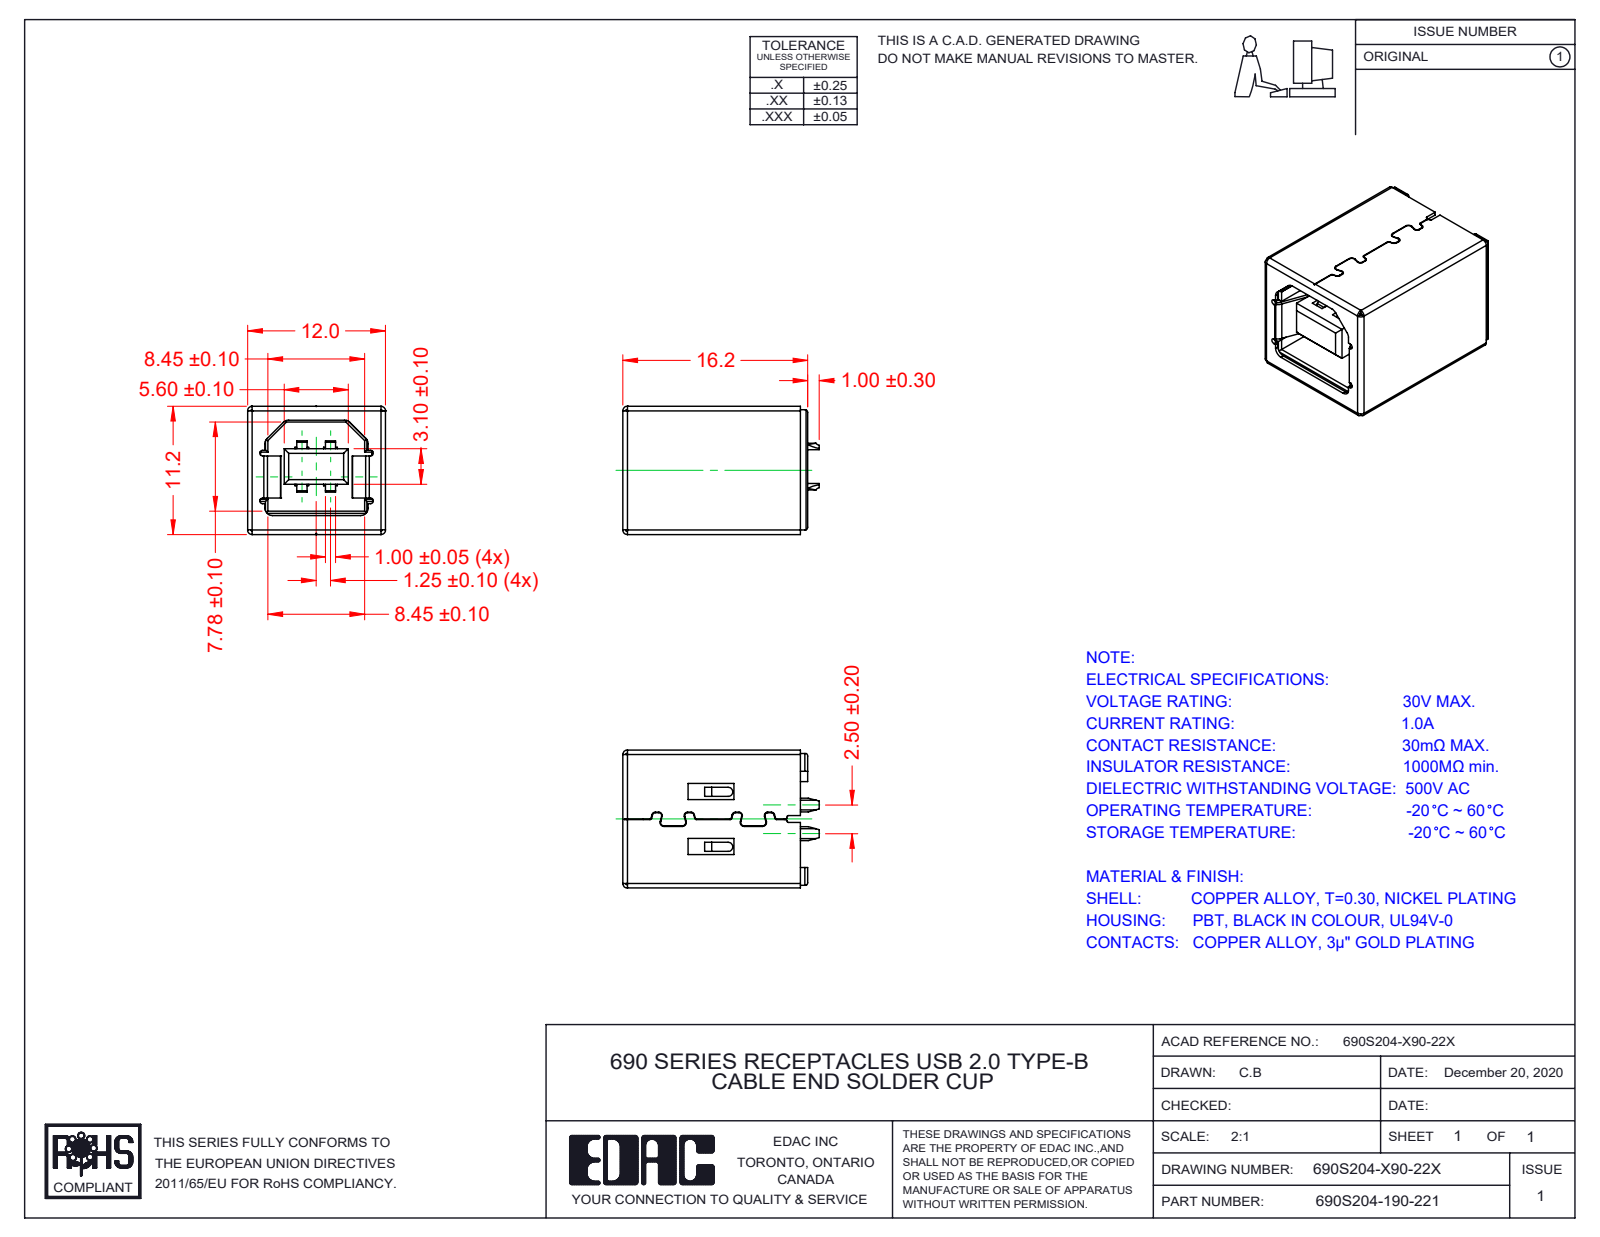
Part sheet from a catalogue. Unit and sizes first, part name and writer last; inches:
Units: inches
Overall size (bounding box): 0.675 × 0.474 × 0.441
Partial cylindrical surfaces — rounded edges, fillets, slot ends (radius × count): R0.01 ×19, R0.012 ×14, R0.016 ×12, R0.004 ×11, R0.008 ×8, R0.014 ×8, R0.006 ×6, R0.026 ×6
Main face-to-face distances: 0.429, 0.462, 0.417, 0.453, 0.45, 0.465, 0.474, 0.441, 0.081, 0.016
Volume: 0.083 in³ · Surface area: 5.234 in²
Bodies: 6 solids, 629 faces (428 planar, 201 cylindrical, 0 other)
Part name (STEP PRODUCT): Shell 690S204-X90-22X; Contact 690S204-X90-22X; Insulator 690S204-X90-22X_Black; 690S204-190-221
STEP written by: SolidWorks 2020 (AUTOMOTIVE_DESIGN)
